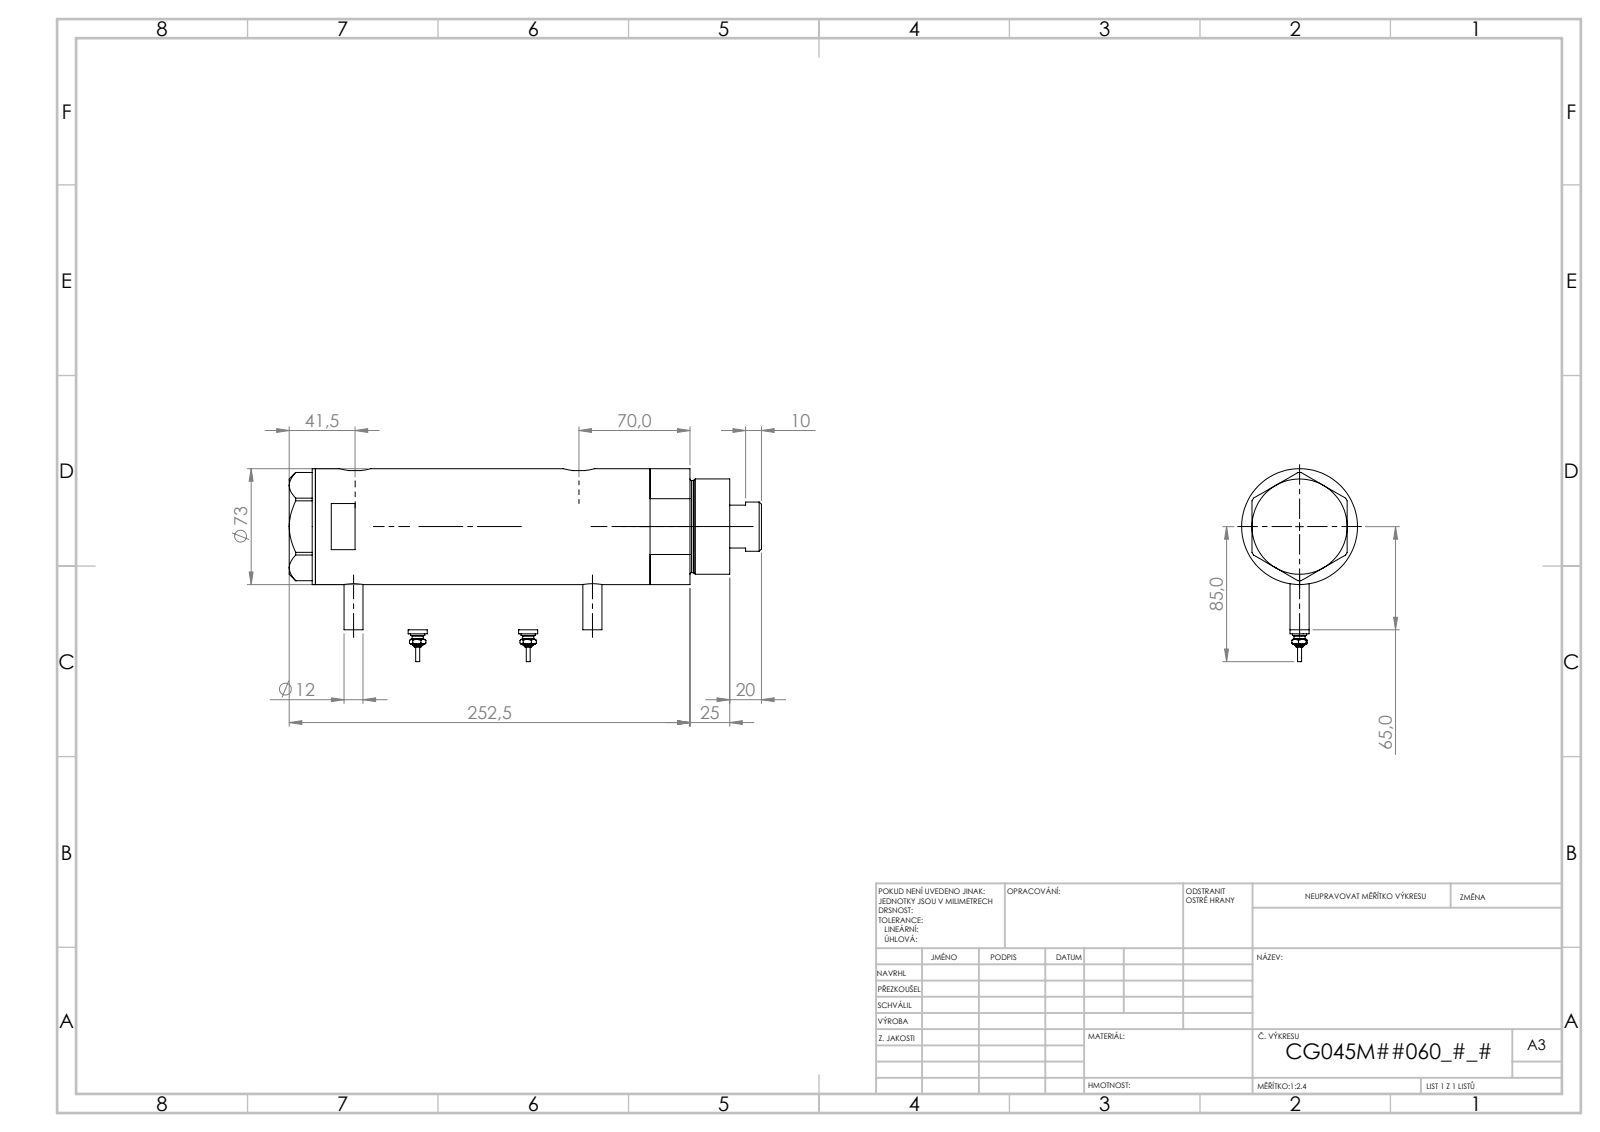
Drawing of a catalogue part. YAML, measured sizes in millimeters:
part_name: "V270CG_FRONT; V270CG_SWITCH; V270CG_MIDDLE; V270CG_VC (+1 more)"
step_written_by: "SolidWorks 2019 (CONFIG_CONTROL_DESIGN)"
units: millimeters
bodies: {solids: 6, faces: 231, planar: 78, cylindrical: 79, other: 74}
overall_size: [251.52, 105.3, 73]
volume: 873564
surface_area: 150161
round_holes:
  - {diameter: 5, count: 2}
  - {diameter: 12.5, count: 2}
  - {diameter: 13.16, count: 2}
  - {diameter: 10.5, count: 1}
  - {diameter: 32, count: 1}
  - {diameter: 33.5, count: 1}
  - {diameter: 45, count: 1}
  - {diameter: 48, count: 1}
  - {diameter: 64, count: 1}
round_bosses_or_shafts:
  - {diameter: 12, count: 3}
  - {diameter: 9, count: 2}
  - {diameter: 7, count: 2}
  - {diameter: 4.34, count: 2}
  - {diameter: 2.4, count: 2}
  - {diameter: 73, count: 1}
  - {diameter: 60, count: 1}
  - {diameter: 58, count: 1}
partial_cylinders:
  - {radius: 10, count: 2}
face_to_face_distances: [127.14, 16.5, 143.64, 60, 215.01, 231.51, 87.87, 42.5, 26, 101.14]
hole_center_spacings: [111.65, 0.99, 1, 8.5, 8.51, 102.15, 103.14, 103.15]
